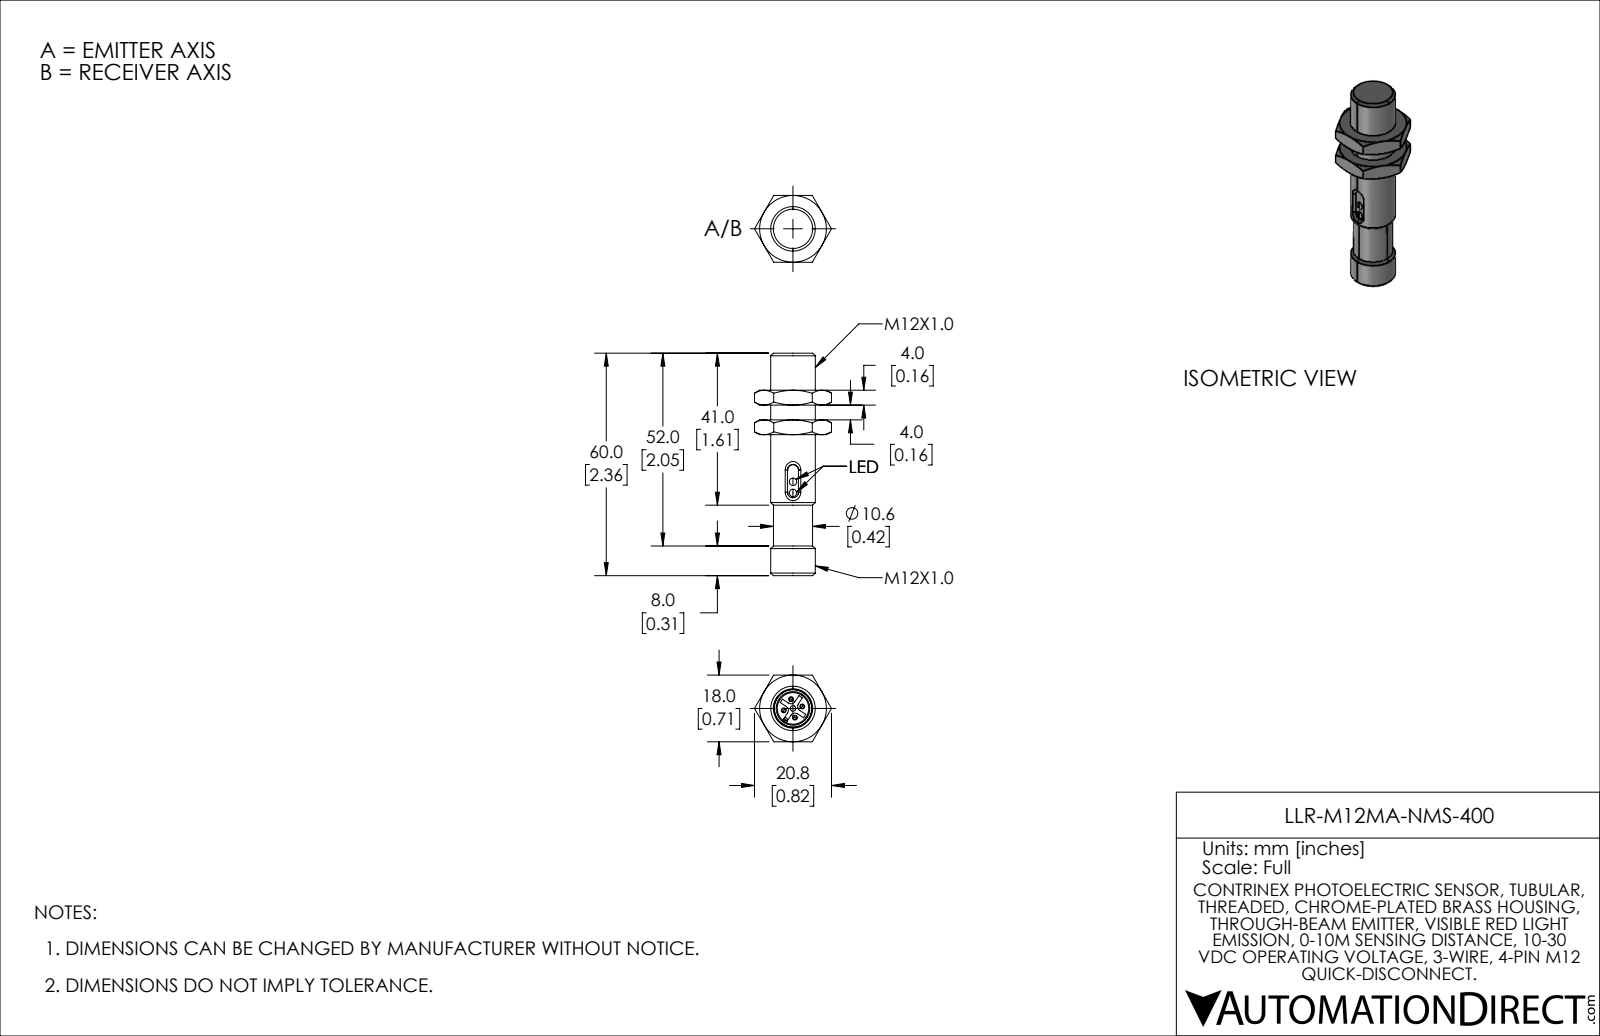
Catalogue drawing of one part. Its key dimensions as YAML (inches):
part_name: "LLR-M12MA-NMS-400"
step_written_by: "SolidWorks 2021 (AUTOMOTIVE_DESIGN)"
units: inches
bodies: {solids: 3, faces: 169, planar: 44, cylindrical: 54, other: 71}
overall_size: [2.362, 0.819, 0.709]
volume: 0.457
surface_area: 6.518
round_holes:
  - {diameter: 0.059, count: 1}
  - {diameter: 0.335, count: 1}
  - {diameter: 0.402, count: 1}
  - {diameter: 0.472, count: 1}
round_bosses_or_shafts:
  - {diameter: 0.039, count: 4}
  - {diameter: 0.415, count: 1}
partial_cylinders:
  - {radius: 0.049, count: 4}
  - {radius: 0.02, count: 2}
  - {radius: 0.059, count: 2}
  - {radius: 0.022, count: 1}
face_to_face_distances: [0.157, 0.709, 0.315, 0.472, 0.551, 0.394, 0.866, 2.016, 1.622, 1.465]
